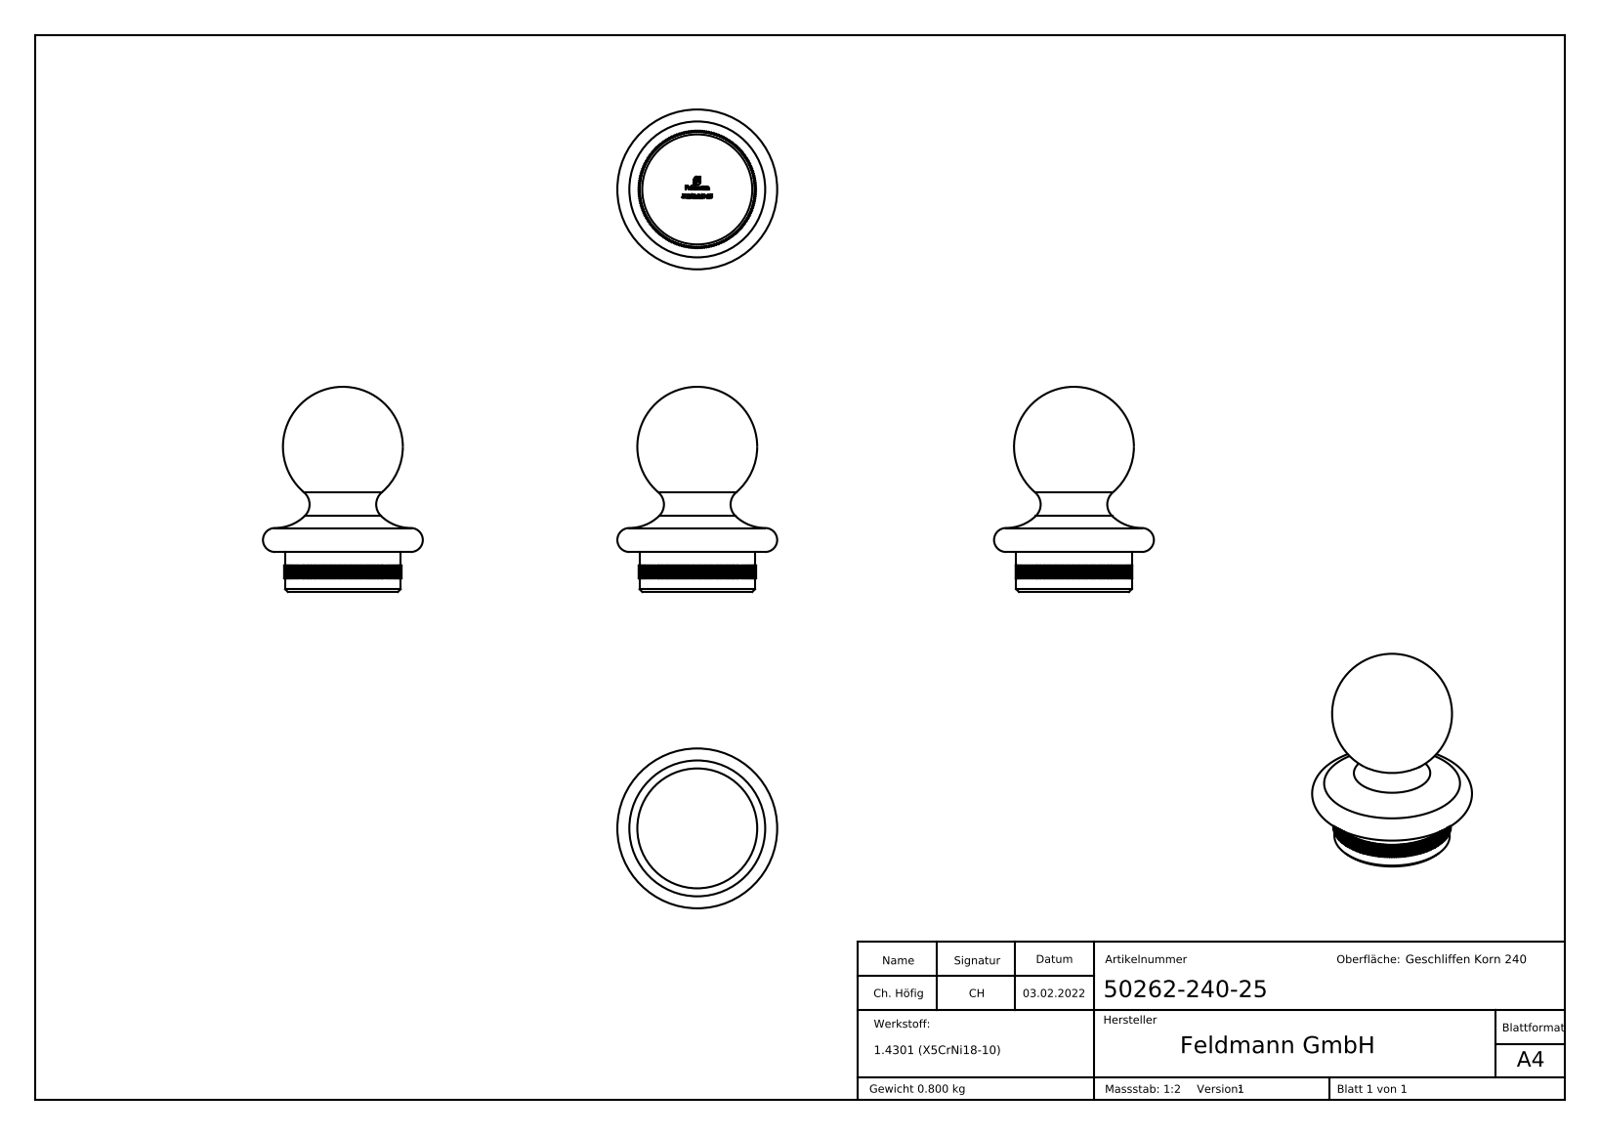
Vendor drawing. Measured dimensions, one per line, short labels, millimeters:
name: 50262-240-25
written by: SolidWorks 2018 (CONFIG_CONTROL_DESIGN)
unit: mm
bodies: 1 solid, 1197 faces (1046 planar, 4 cylindrical, 147 other)
size: 77 × 60 × 60
volume: 101 207 mm³; area: 14 825 mm²
bosses: 1× ⌀43.3
face distances: 15, 30.62, 30.63, 30.6, 30.64, 5, 30.61, 10, 4.9, 9.9
